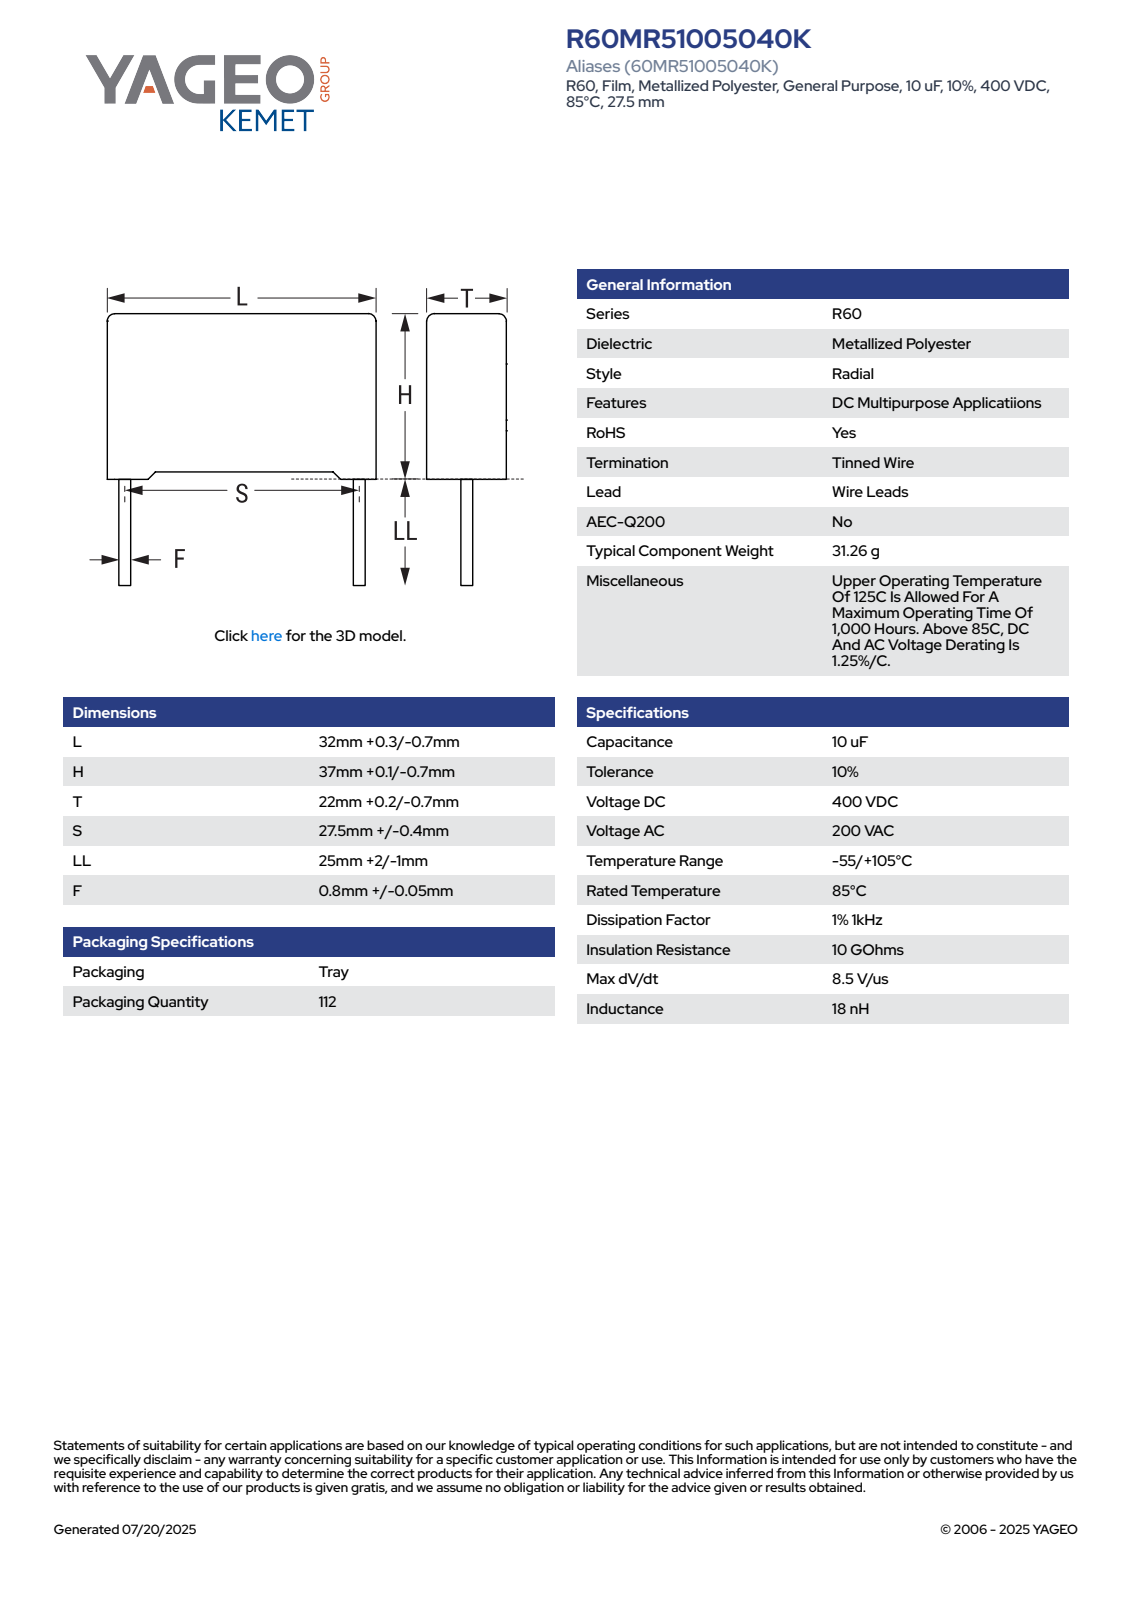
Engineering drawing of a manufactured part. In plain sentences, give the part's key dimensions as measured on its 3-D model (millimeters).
The part is named "CFR_RB2_32X37X22_L32.3H37.1T22.2S27.5LL27F0.85". Its 3-D file was written by "SolidWorks 2021 (AUTOMOTIVE_DESIGN)". It is 4 solids with 85 faces: 77 planar, 8 cylindrical and 0 other. Overall it measures 64.1 by 32.3 by 22.2 millimeters. Its volume is 25 866 cubic millimeters and its surface area 5 674 square millimeters. Round bosses or shafts: 2 of diameter 0.85. Partial cylindrical surfaces (rounded edges, fillets, slot ends): 4 of radius 0.5. The main face-to-face distances are 22.2, 32.3, 35.82, 0.53, 36.35, 0.75, 1.28, 37.1, 1.08, 31.22.
